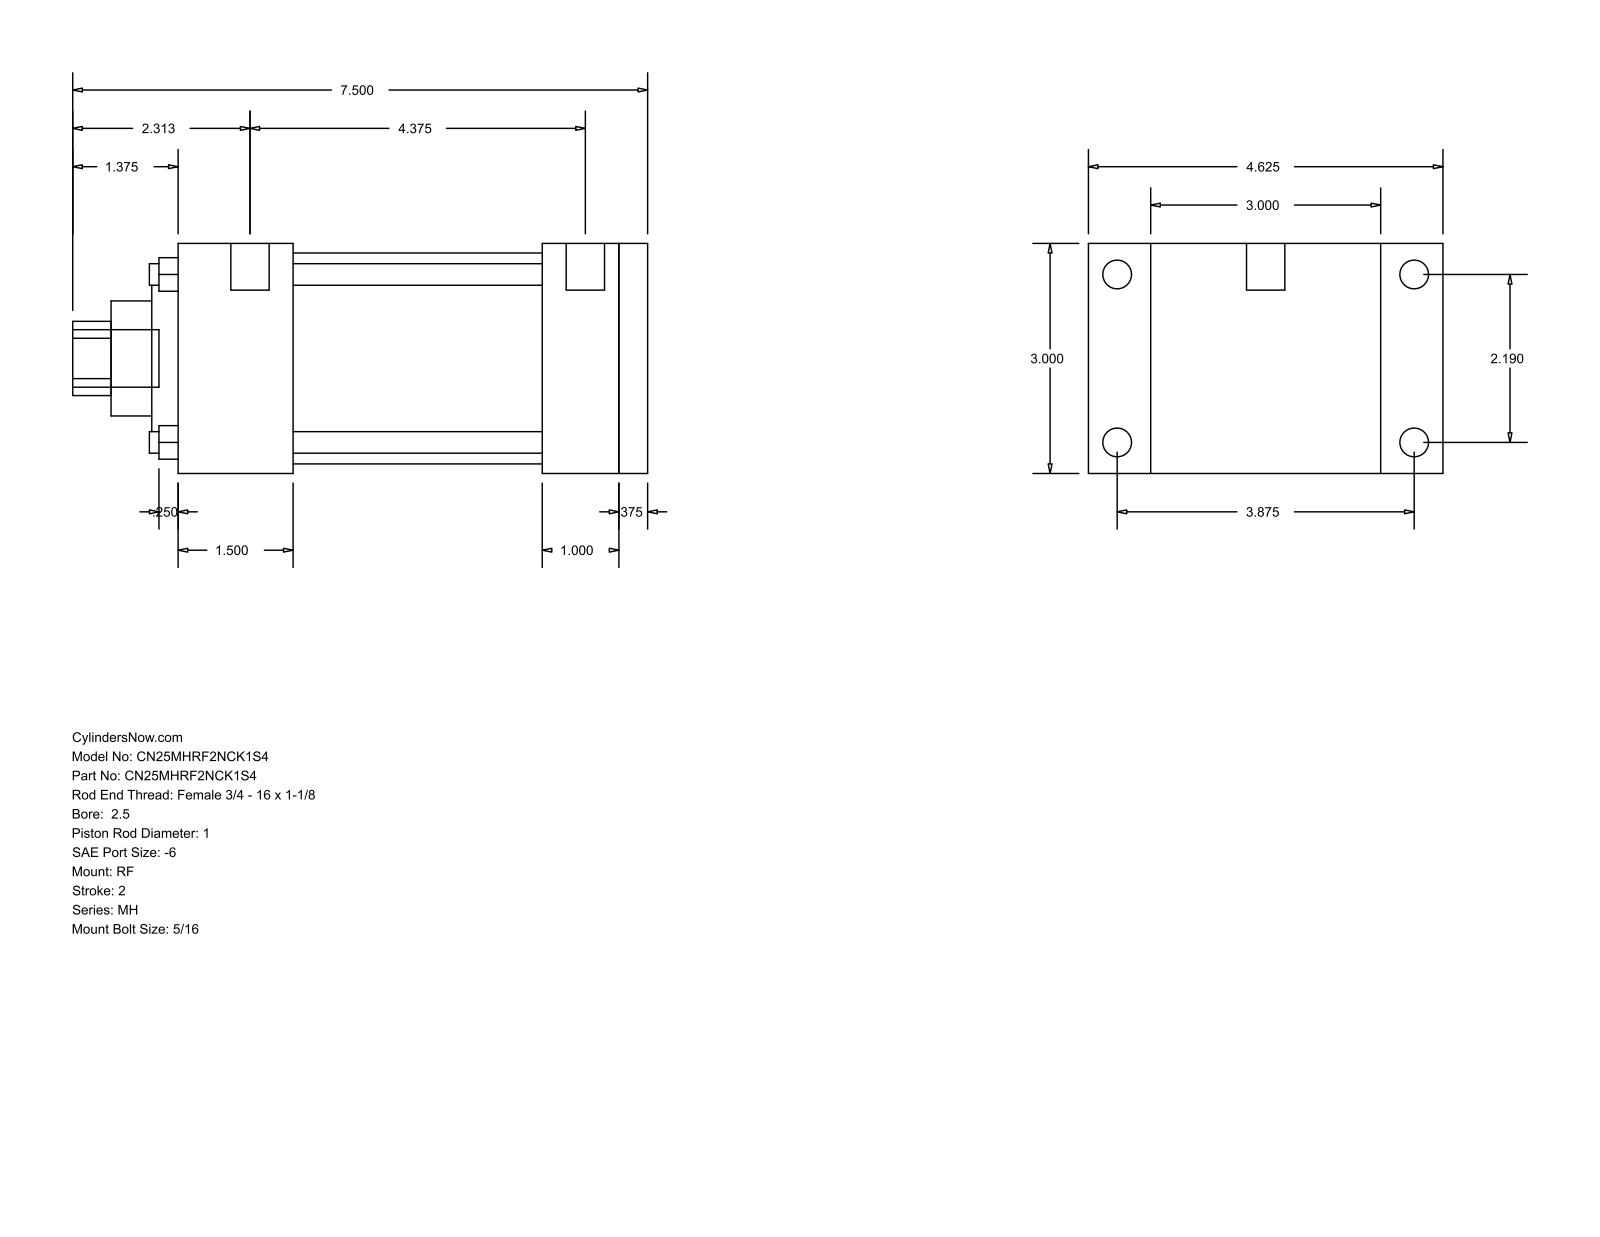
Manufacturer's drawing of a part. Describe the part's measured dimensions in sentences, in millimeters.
The part is named "MH_RF__0250_1". Its 3-D file was written by "GSSL Pune (CONFIG_CONTROL_DESIGN)". It is 0 solids with 94 faces: 65 planar, 29 cylindrical and 0 other. Overall it measures 190.5 by 117.47 by 76.2 millimeters. Round holes: 4 of diameter 7.14, 1 of diameter 25.4, 1 of diameter 38.1, 1 of diameter 60.33, 1 of diameter 69.85. Round bosses or shafts: 4 of diameter 9.53, 4 of diameter 5.56, 2 of diameter 12.7, 1 of diameter 19.05. Partial cylindrical surfaces (rounded edges, fillets, slot ends): 1 of radius 12.29. The main face-to-face distances are 76.2, 9.53, 146.05, 155.58, 25.4, 120.65, 34.93, 38.11, 82.54, 107.94. The hole center spacings are 39.33, 55.62, 78.66.
